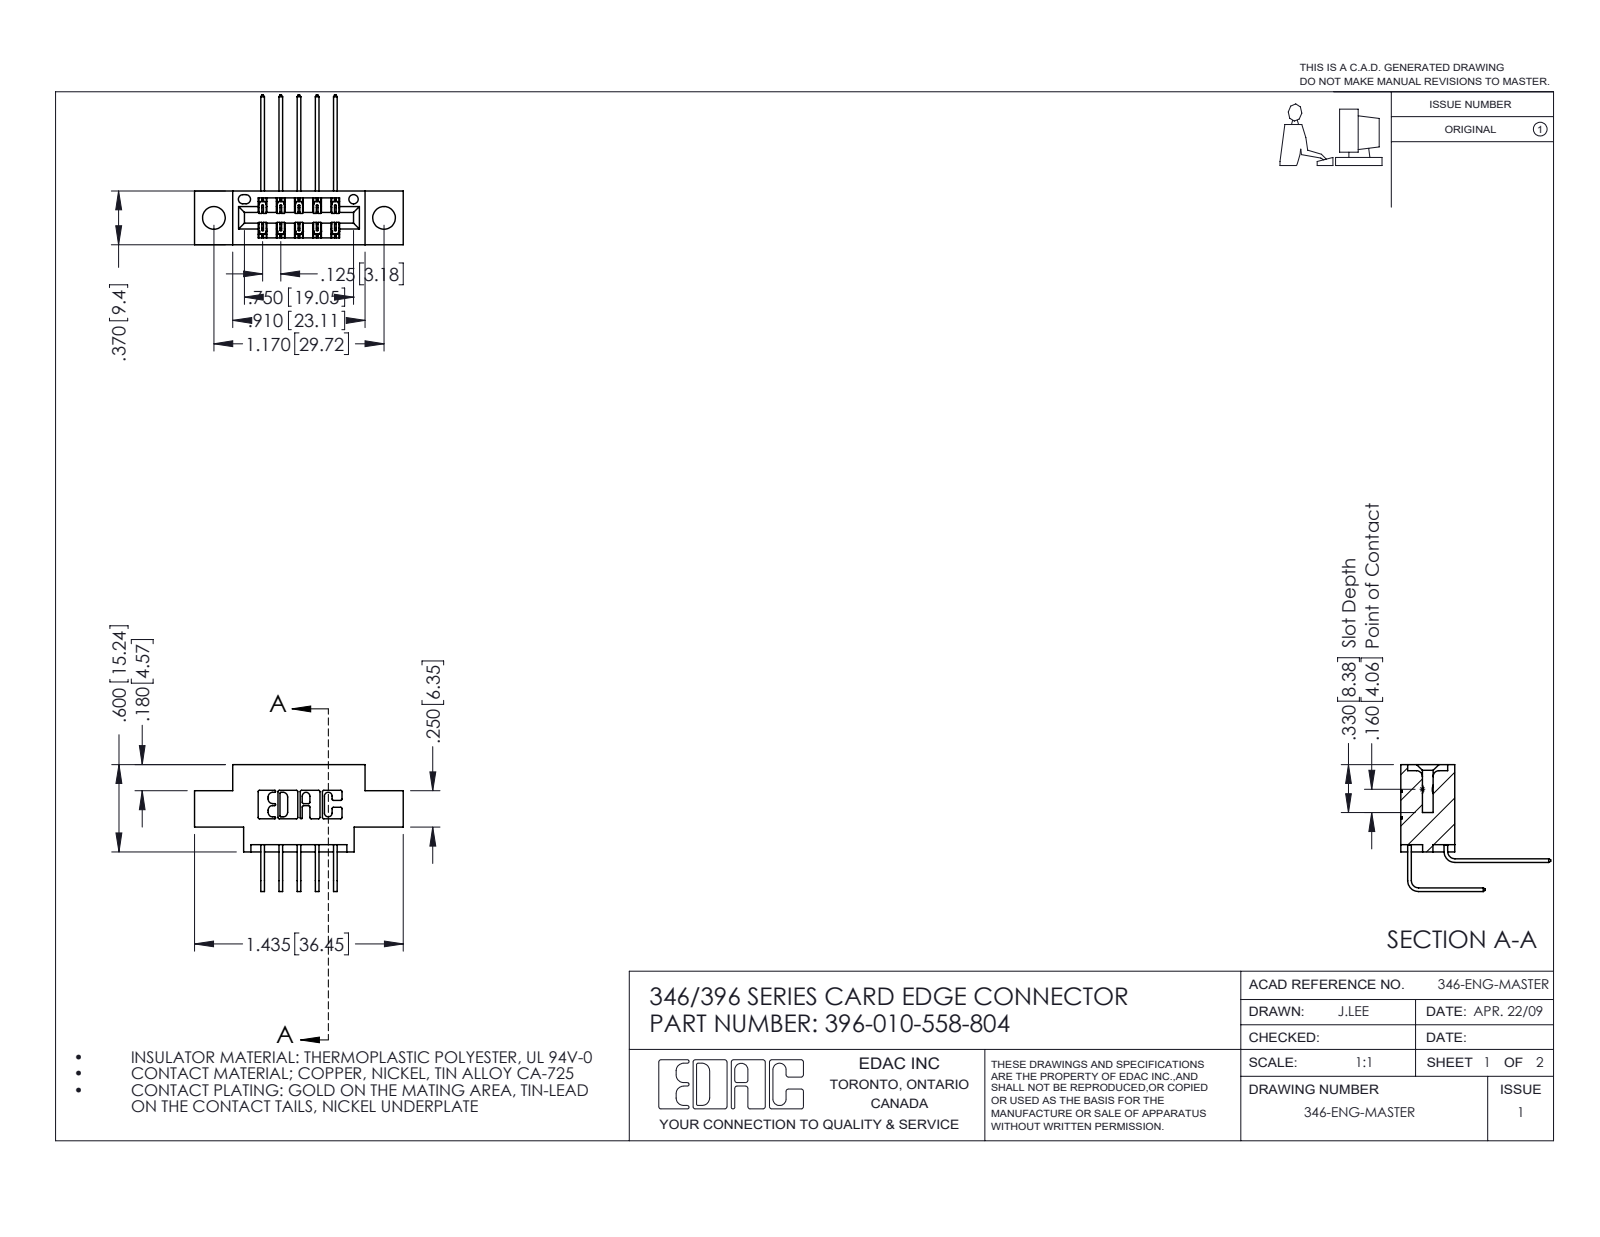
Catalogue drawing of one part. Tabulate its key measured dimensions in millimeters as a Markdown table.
| quantity | value |
| --- | --- |
| part name | 346 Part_0.170 Offset - 0.156 Dia-TH; 396-010-558-804; 345-292-001_558 Tail - 2; 345-292-001_558 559 Tail - 1 |
| STEP written by | SolidWorks 2016 (CONFIG_CONTROL_DESIGN) |
| units | millimeters |
| bodies | 11 solids, 666 faces (450 planar, 216 cylindrical, 0 other) |
| overall size | 36.4 × 26.2 × 22.2 |
| volume | 3 080 mm³ |
| surface area | 3 925 mm² |
| round holes (diameter × count) | 4 × 2, 1.6 × 1 |
| partial cylindrical surfaces (radius × count) | 0.3 × 22, 0.2 × 15, 0.2 × 6, 0.8 × 6, 0.7 × 3, 0.4 × 2, 0.6 × 2, 0.6 × 2 |
| main face-to-face distances | 6.4, 9.4, 1.2, 8.2, 0.6, 1.8, 7.6, 3.2, 3.8, 5.6 |
| hole center spacings | 6.2, 24.6, 29.7 |
